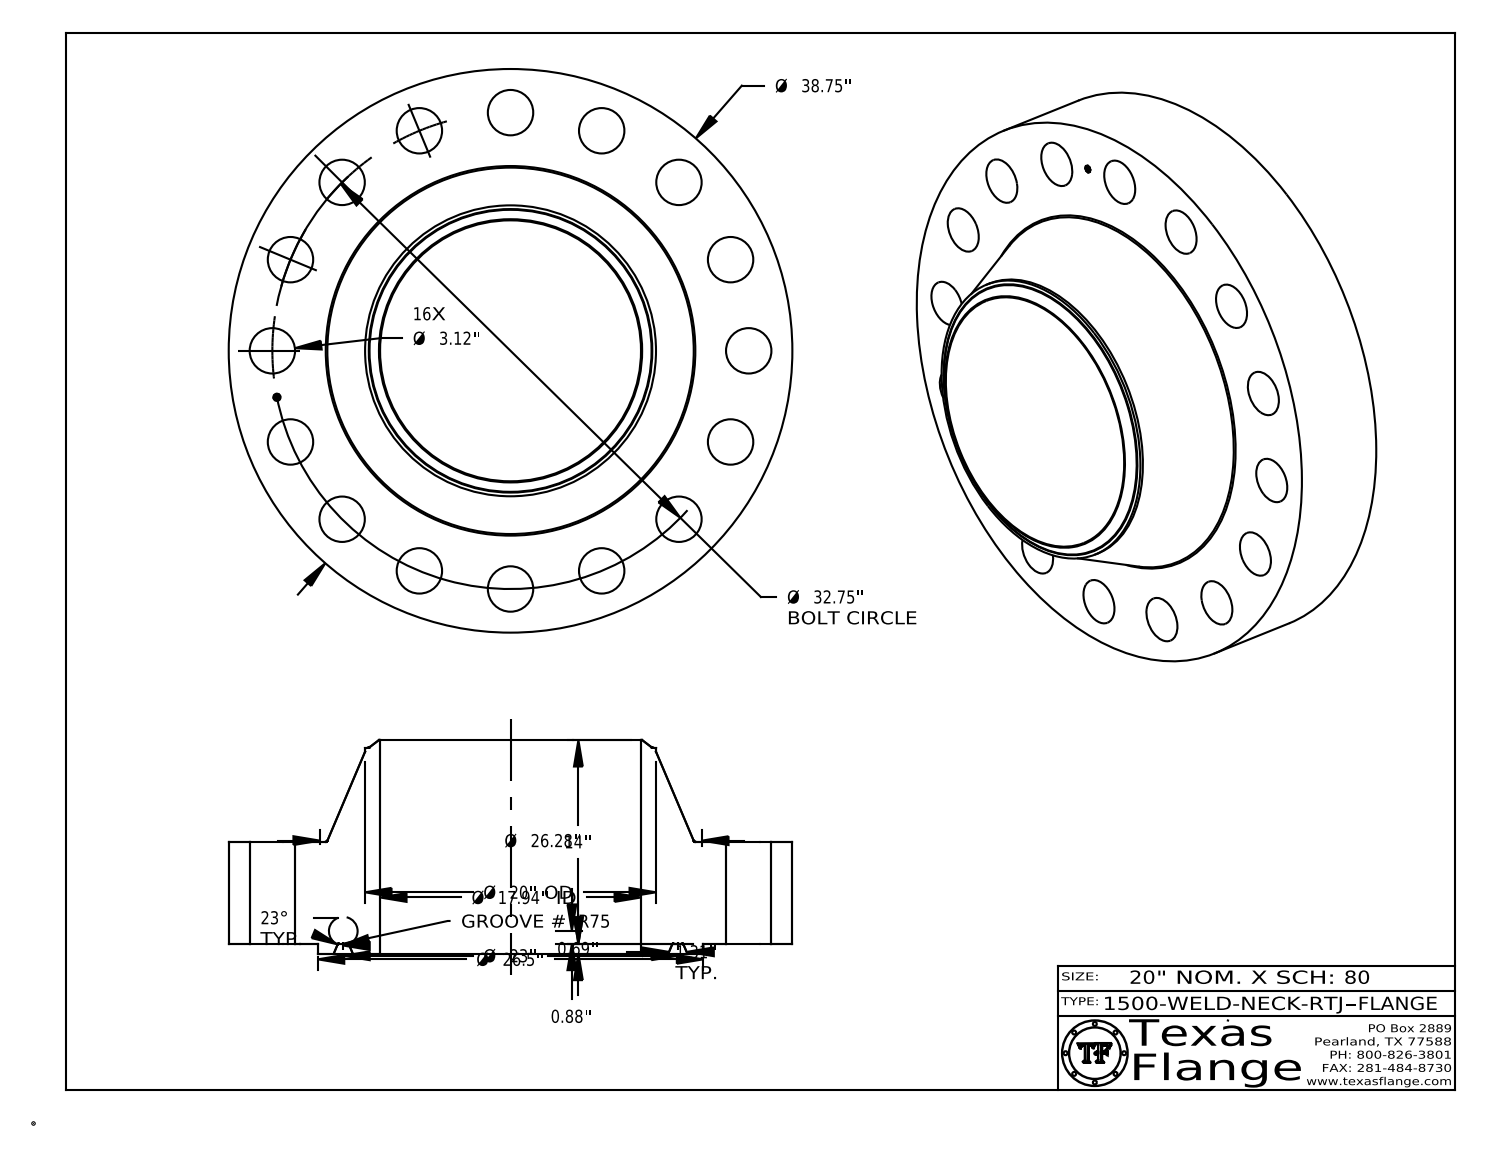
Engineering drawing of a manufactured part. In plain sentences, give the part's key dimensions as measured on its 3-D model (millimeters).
The part is named "1500-WELD-NECK-RTJ". Its 3-D file was written by "CATIA V5 STEP AP214 (AUTOMOTIVE_DESIGN)". It is 1 solid with 449 faces: 371 planar, 60 cylindrical and 18 other. Overall it measures 984.3 by 984.3 by 373.1 millimeters. Its volume is 110 600 000 cubic millimeters and its surface area 3 112 000 square millimeters. Round holes: 16 of diameter 79.2, 1 of diameter 12.6, 1 of diameter 455.6. Round bosses or shafts: 8 of diameter 0.8, 1 of diameter 984.3, 1 of diameter 673.1, 1 of diameter 508, 1 of diameter 9.9. The main face-to-face distances are 177.8, 17.5, 195.3, 373.1, 355.6, 194.9, 177.4, 0.4, 178.2, 3.8. The hole center spacings are 462.2, 415.9, 318.3, 588.2, 768.5, 162.3, 162.3, 691.6.
